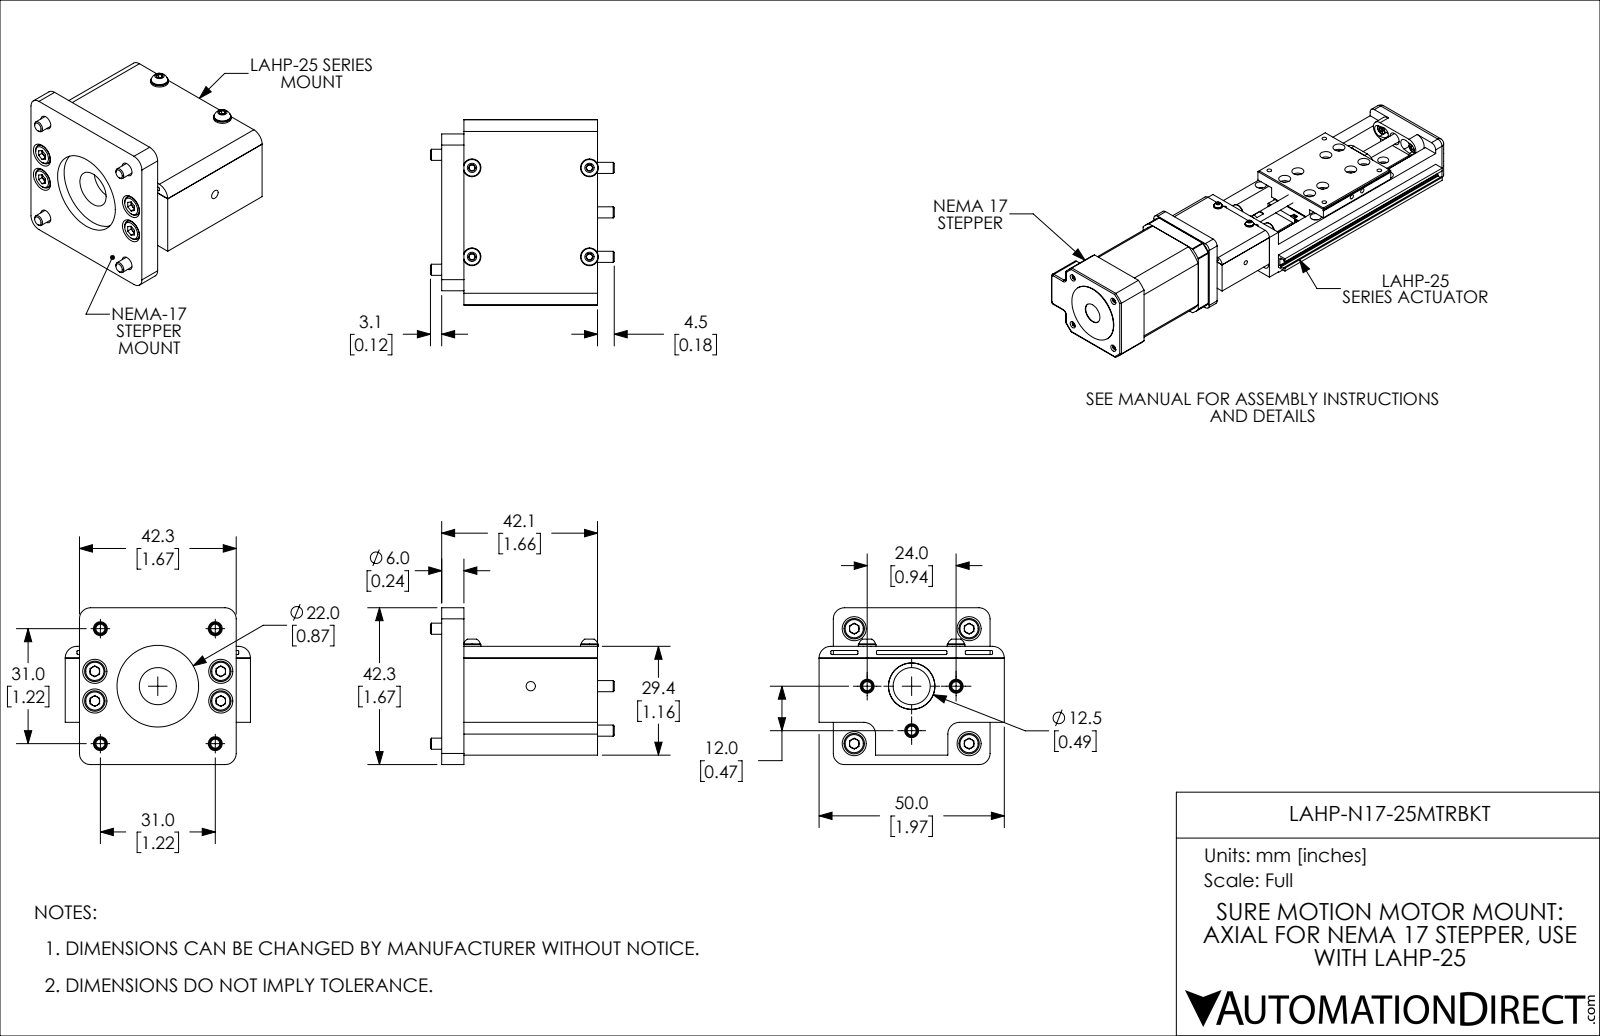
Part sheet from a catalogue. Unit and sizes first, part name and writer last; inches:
Units: inches
Overall size (bounding box): 1.969 × 1.953 × 1.665
Round holes (diameter × count): ⌀0.126 ×11, ⌀0.148 ×11, ⌀0.256 ×11, ⌀0.098 ×5, ⌀0.081 ×4, ⌀0.106 ×4, ⌀0.122 ×4, ⌀0.394 ×1, ⌀0.493 ×1, ⌀0.867 ×1
Round bosses / shafts (diameter × count): ⌀0.217 ×11, ⌀0.118 ×11, ⌀0.189 ×4, ⌀0.177 ×4, ⌀0.098 ×4, ⌀0.492 ×1
Partial cylindrical surfaces — rounded edges, fillets, slot ends (radius × count): R0.01 ×12, R0.125 ×12, R0.118 ×4
Main face-to-face distances: 0.125, 0.236, 1.42, 0.08, 0.045, 1.656, 0.682, 0.762, 0.807, 0.065
Hole centre spacings: 0.626, 1.243, 0.252, 0.457, 0.687, 0.77, 0.863, 1.152
Volume: 2.152 in³ · Surface area: 38.23 in²
Bodies: 33 solids, 715 faces (315 planar, 236 cylindrical, 164 other)
Part name (STEP PRODUCT): LAHP-N17-25MTRBKT
STEP written by: SolidWorks 2019 (CONFIG_CONTROL_DESIGN)
